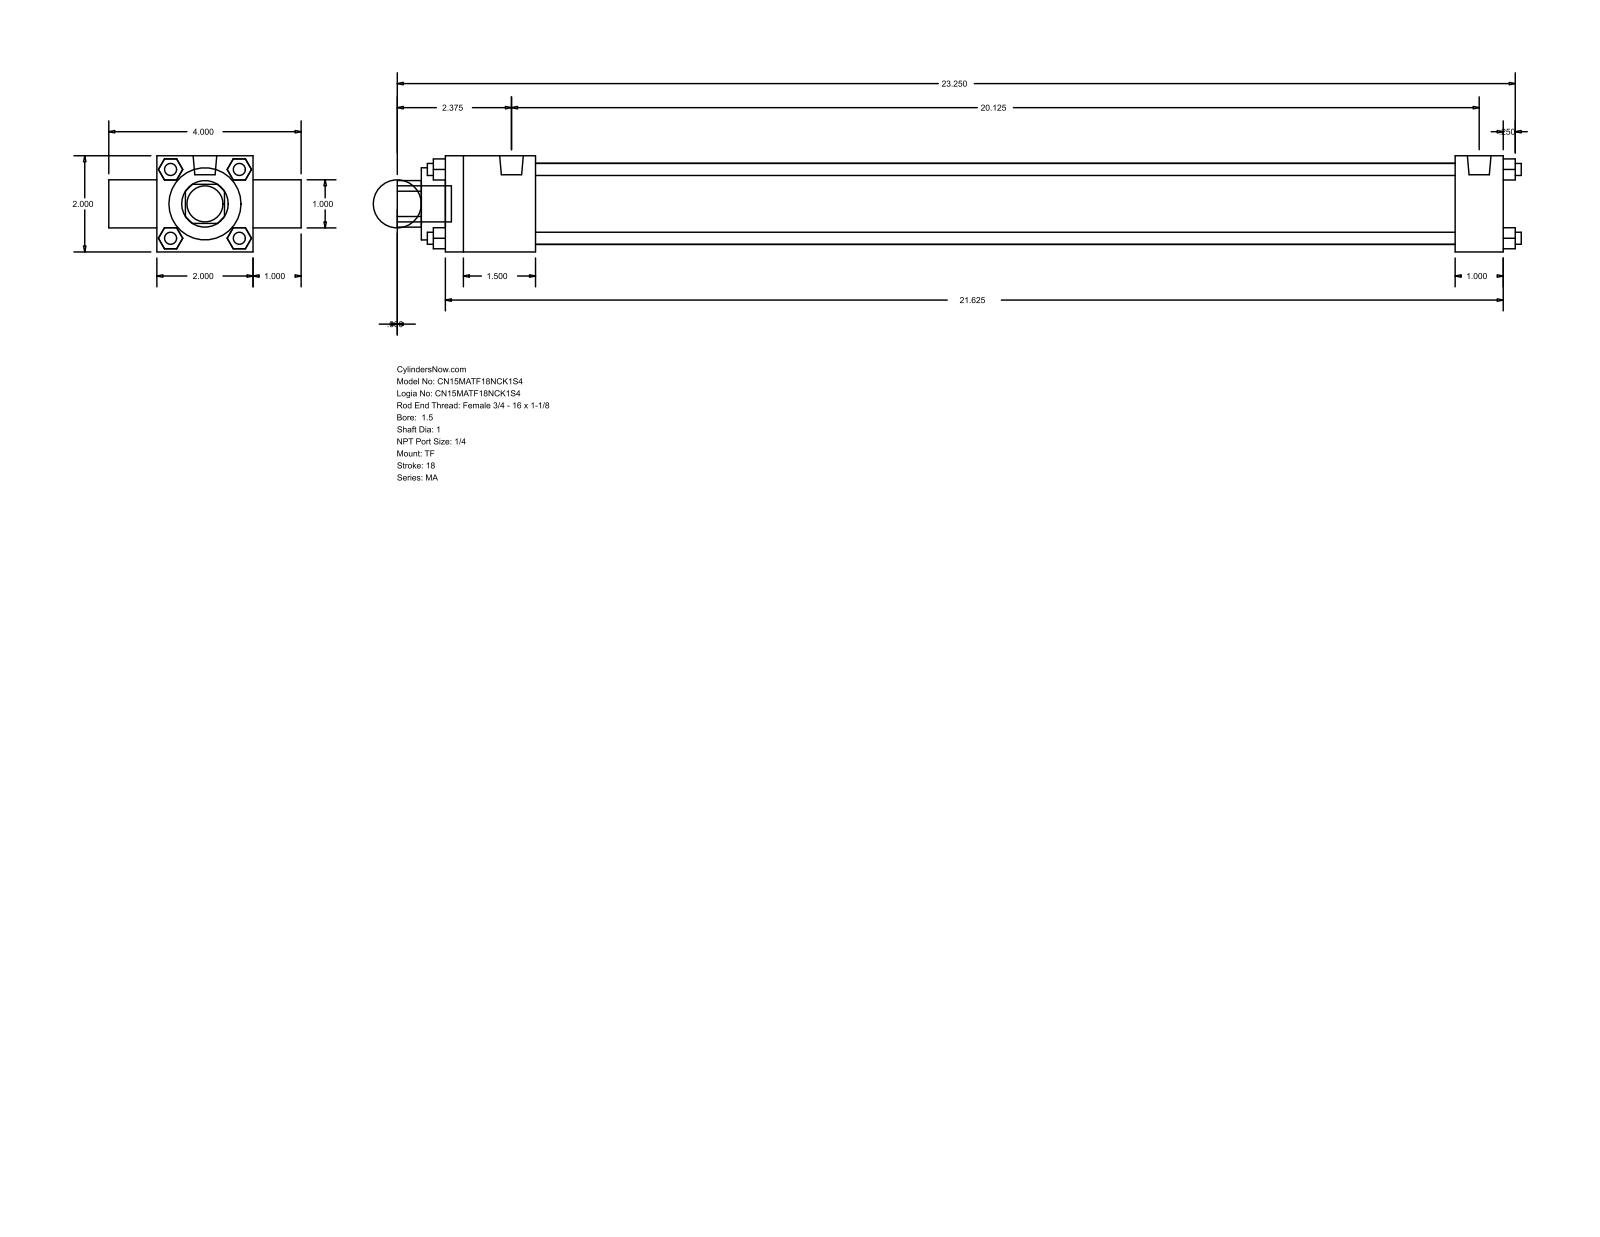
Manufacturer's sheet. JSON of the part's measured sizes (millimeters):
{"part_name": "MA_TF__0150_1", "step_written_by": "GSSL Pune (CONFIG_CONTROL_DESIGN)", "units": "millimeters", "bodies": {"solids": 0, "faces": 120, "planar": 92, "cylindrical": 28, "other": 0}, "overall_size": [593.73, 101.6, 50.8], "round_holes": [[25.4, 2], [38.1, 1], [42.93, 1]], "round_bosses_or_shafts": [[6.35, 4], [7.94, 3], [12.49, 2], [19.05, 1]], "partial_cylinders_radius": [[12.29, 1]], "face_to_face_distances": [50.8, 25.4, 558.8, 76.2, 6.35, 47.63, 533.4, 485.77, 511.17, 571.5]}
